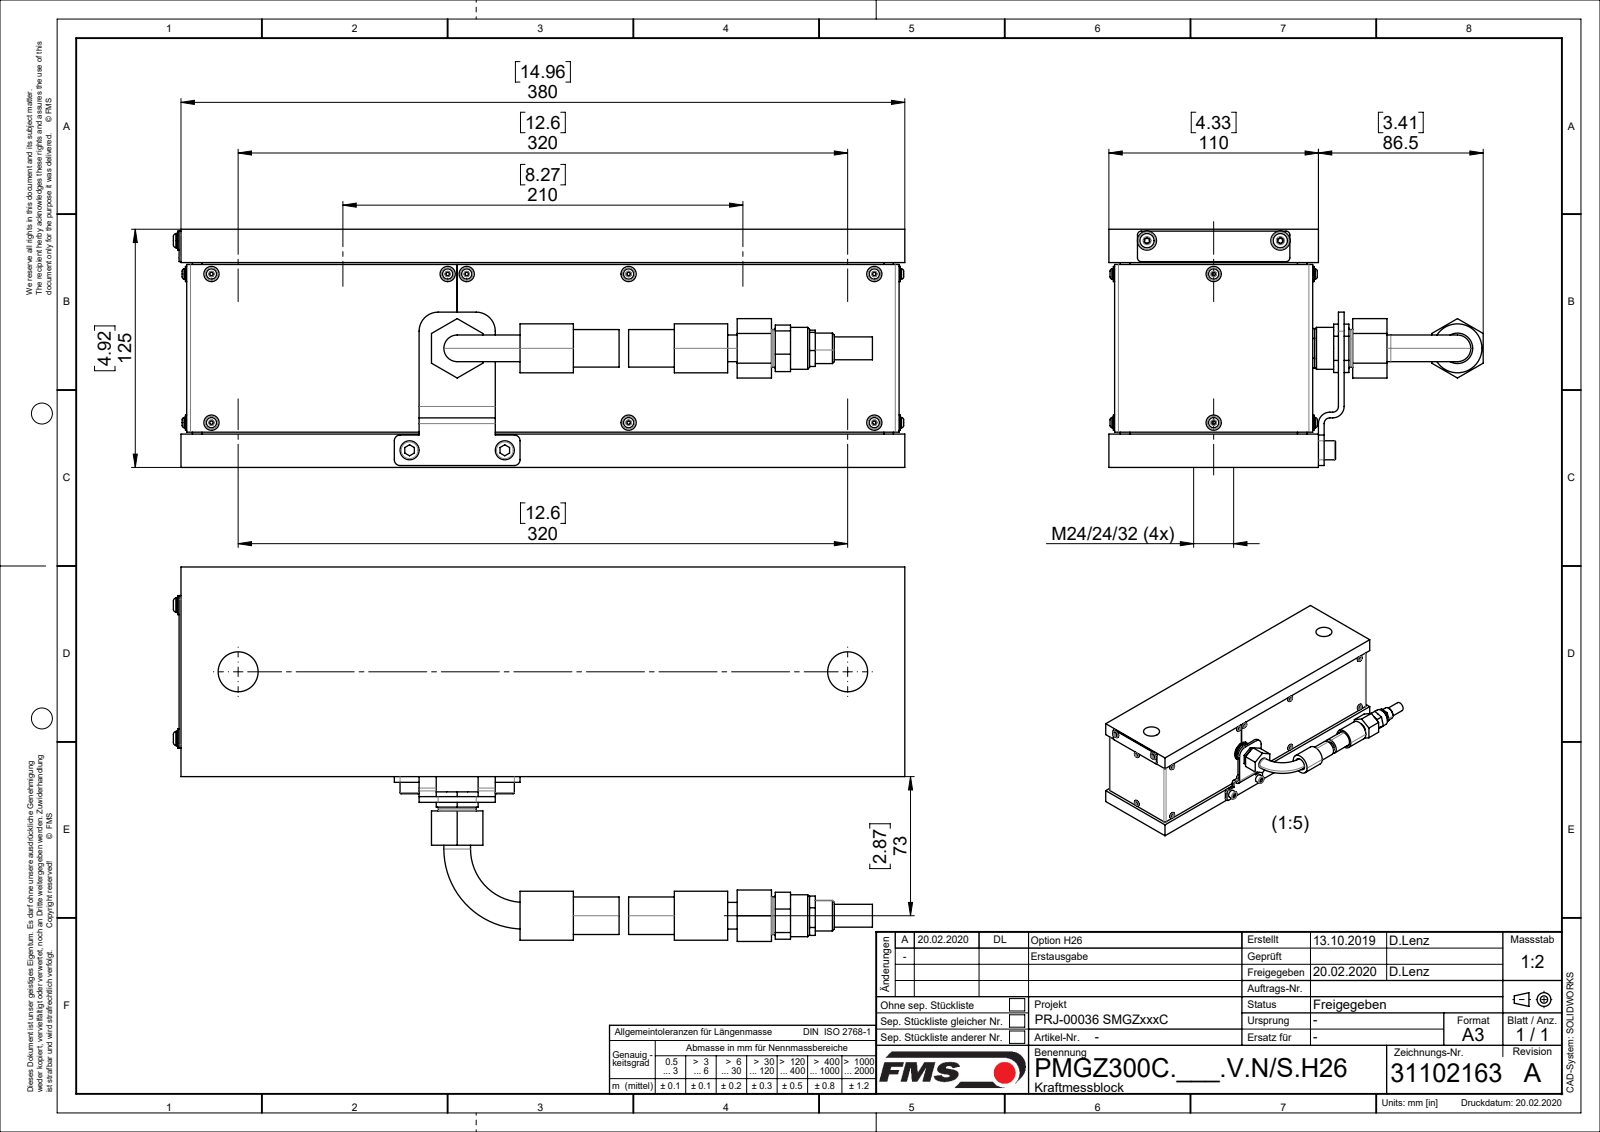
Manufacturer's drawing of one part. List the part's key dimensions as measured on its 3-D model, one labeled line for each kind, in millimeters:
Part name (STEP PRODUCT): Ls-Schr eco-fix BN10649_M4x8; 31101665_01; Ls-Schr eco-fix BN10649_M3x8; Hydraulikschlauch_01 (+8 more)
STEP written by: SolidWorks 2018 (CONFIG_CONTROL_DESIGN)
Units: millimetres
Bodies: 53 solids, 1661 faces (390 planar, 1027 cylindrical, 244 other)
Overall size (bounding box): 384 × 196.5 × 125
Volume: 4 901 000 mm³ · Surface area: 653 170 mm²
Round holes (diameter × count): ⌀4 ×21, ⌀5.4 ×18, ⌀2.5 ×16, ⌀10 ×3, ⌀3.3 ×2, ⌀4.2 ×2, ⌀5 ×2, ⌀6.5 ×2, ⌀7.5 ×2, ⌀9 ×2, ⌀12 ×2, ⌀13.5 ×2
Round bosses / shafts (diameter × count): ⌀8 ×18, ⌀3 ×18, ⌀10 ×4, ⌀22 ×2, ⌀19.7 ×2, ⌀17 ×2, ⌀15.5 ×2, ⌀6 ×2
Partial cylindrical surfaces — rounded edges, fillets, slot ends (radius × count): R0.29 ×264, R0.4 ×24, R1 ×20, R2 ×16, R3 ×6, R6 ×2, R10 ×2
Main face-to-face distances: 1, 2, 101, 3, 100, 102, 99, 103, 98, 104
Hole centre spacings: 5, 78.16, 78, 90, 119.1, 10, 59.55, 39.32
